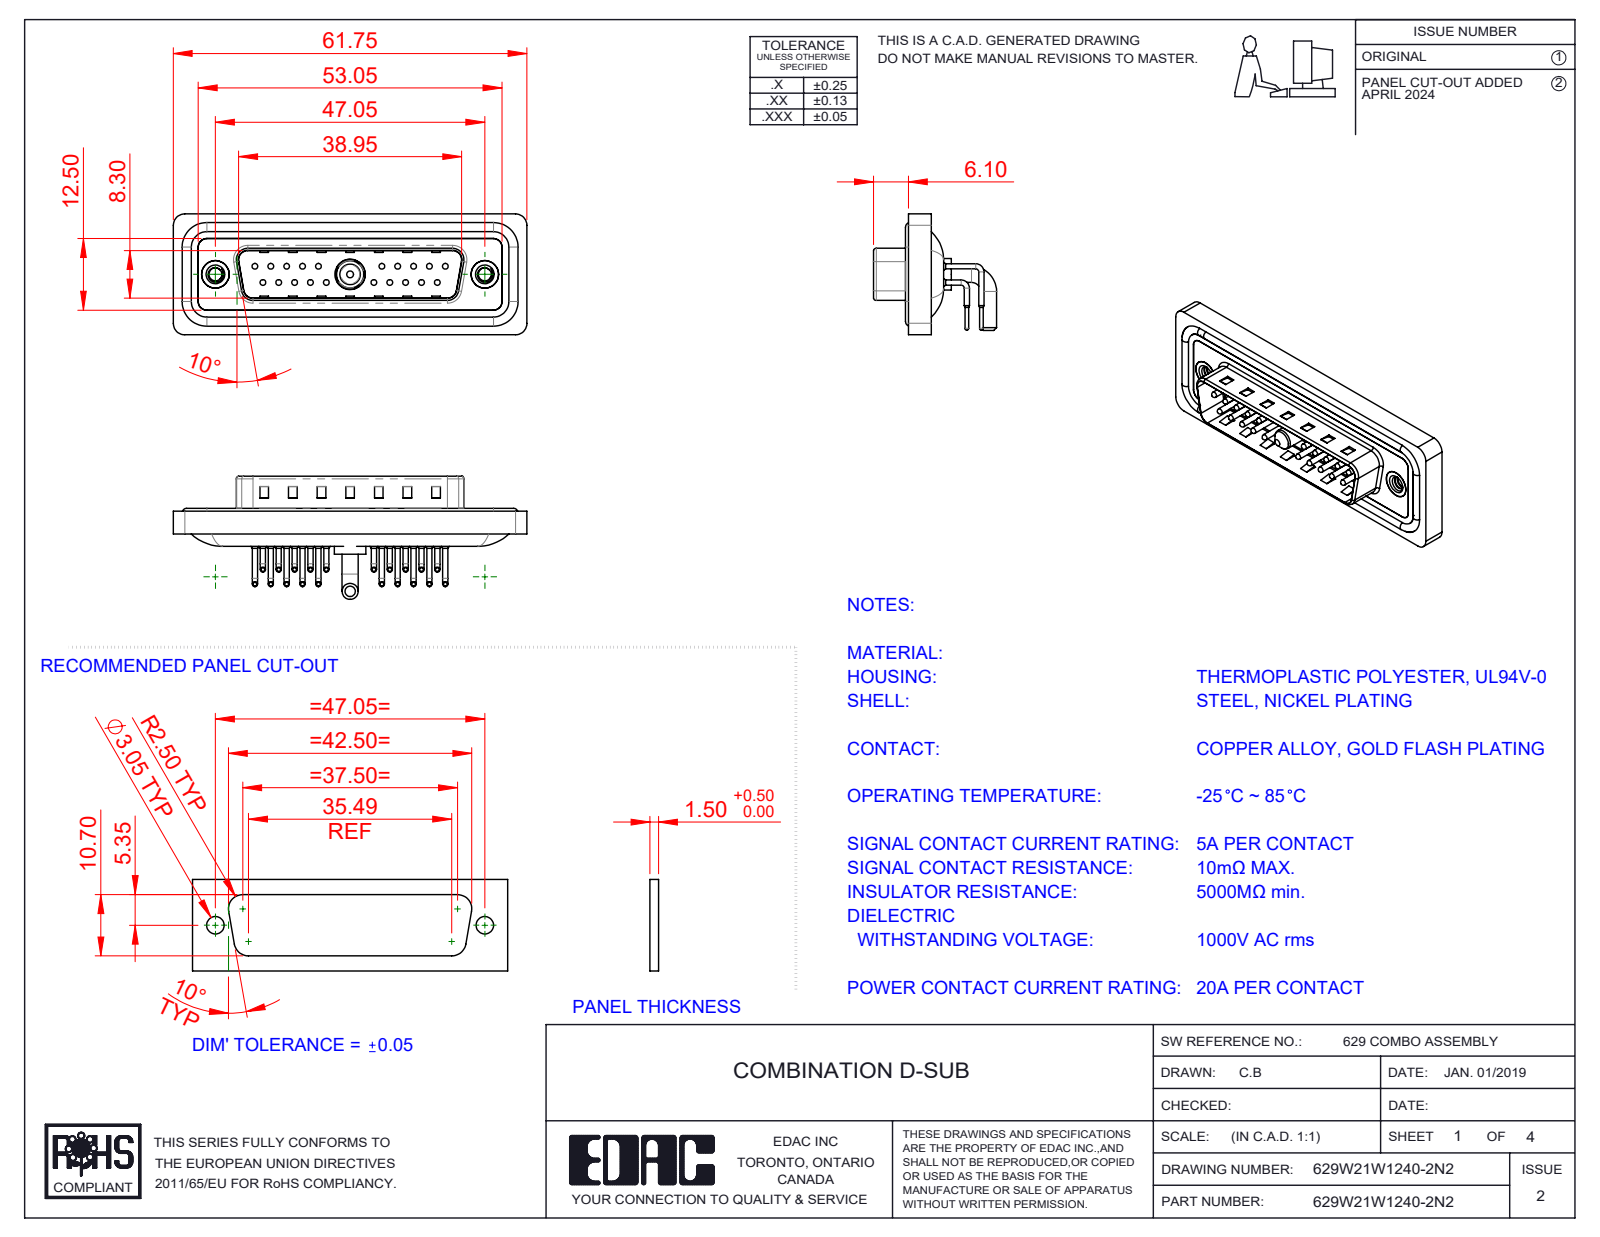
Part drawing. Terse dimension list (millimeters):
name: 629Combo Housing_21W1; 629Combo Contact Row 1; 629Combo Shell Rear_25 Contacts; Power Pin_20A RA (+5 more)
written by: SolidWorks 2023 (CONFIG_CONTROL_DESIGN)
unit: mm
bodies: 29 solids, 2726 faces (1499 planar, 929 cylindrical, 298 other)
size: 61.75 × 21.5 × 21.1
volume: 7 429 mm³; area: 12 721 mm²
holes: 20× ⌀0.75, 20× ⌀1.6, 20× ⌀2, 2× ⌀2.26, 2× ⌀4, 2× ⌀4.8, 2× ⌀5, 1× ⌀4.85, 1× ⌀5.3
bosses: 40× ⌀0.9, 20× ⌀1.5, 20× ⌀1, 20× ⌀0.65, 4× ⌀1.6, 2× ⌀4.9, 2× ⌀2.8, 1× ⌀5.5
rounds: 20× R1.01, 18× R1.5, 18× R2, 8× R0.5, 8× R1.6, 4× R0.25, 4× R0.6, 4× R0.65
face distances: 0.4, 2.9, 0.8, 4.1, 1.1, 2.1, 1.6, 4.5, 1.5, 2.5
hole spacings: 3.16, 2.77, 5.54, 8.31, 5.04, 19.39, 20.97, 22.16
